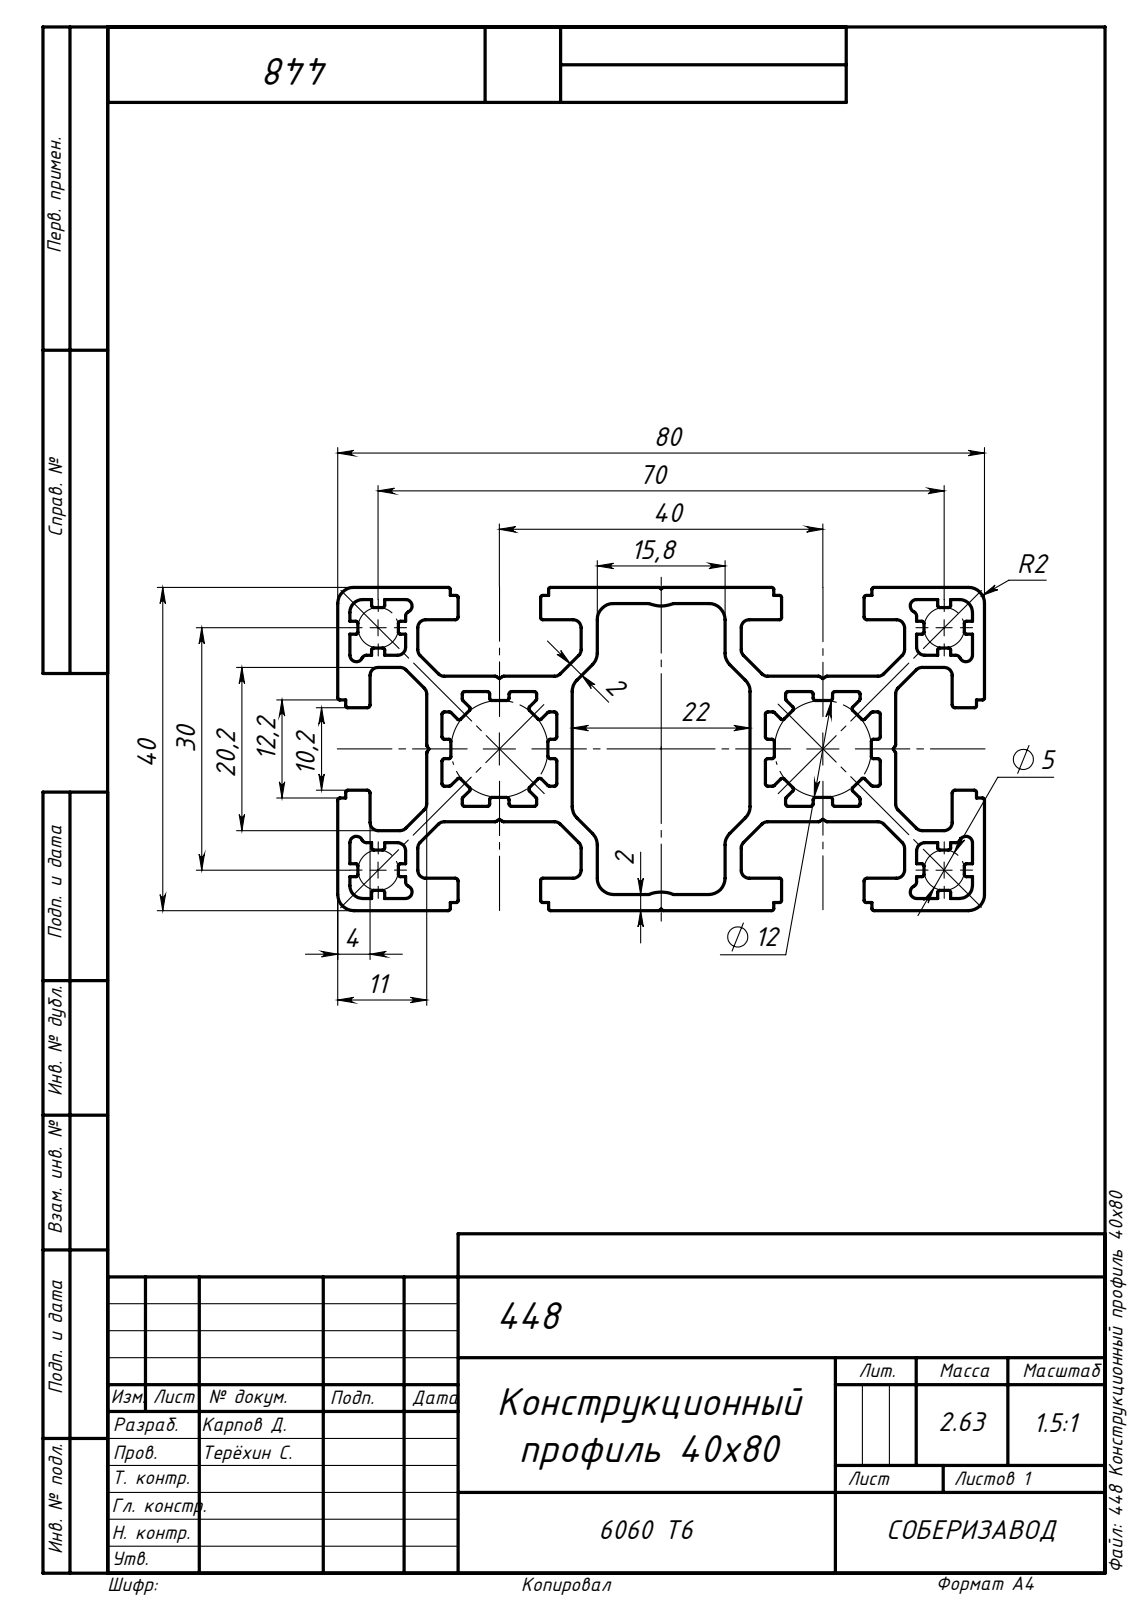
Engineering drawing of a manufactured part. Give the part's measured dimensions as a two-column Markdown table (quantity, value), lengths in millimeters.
| quantity | value |
| --- | --- |
| part name | 448 Конструкционный профиль 40х80 |
| STEP written by | SolidWorks 2019 (AUTOMOTIVE_DESIGN) |
| units | millimeters |
| bodies | 1 solid, 542 faces (288 planar, 254 cylindrical, 0 other) |
| overall size | 1000 × 80 × 40 |
| volume | 974 253 mm³ |
| surface area | 846 148 mm² |
| partial cylindrical surfaces (radius × count) | 0.25 × 88, 0.3 × 64, 1 × 40, 2 × 16, 0.35 × 8, 0.6 × 8, 0.8 × 8, 1.6 × 4 |
| main face-to-face distances | 40, 29, 11, 2, 16.1, 18, 1.9, 4, 7, 25 |
